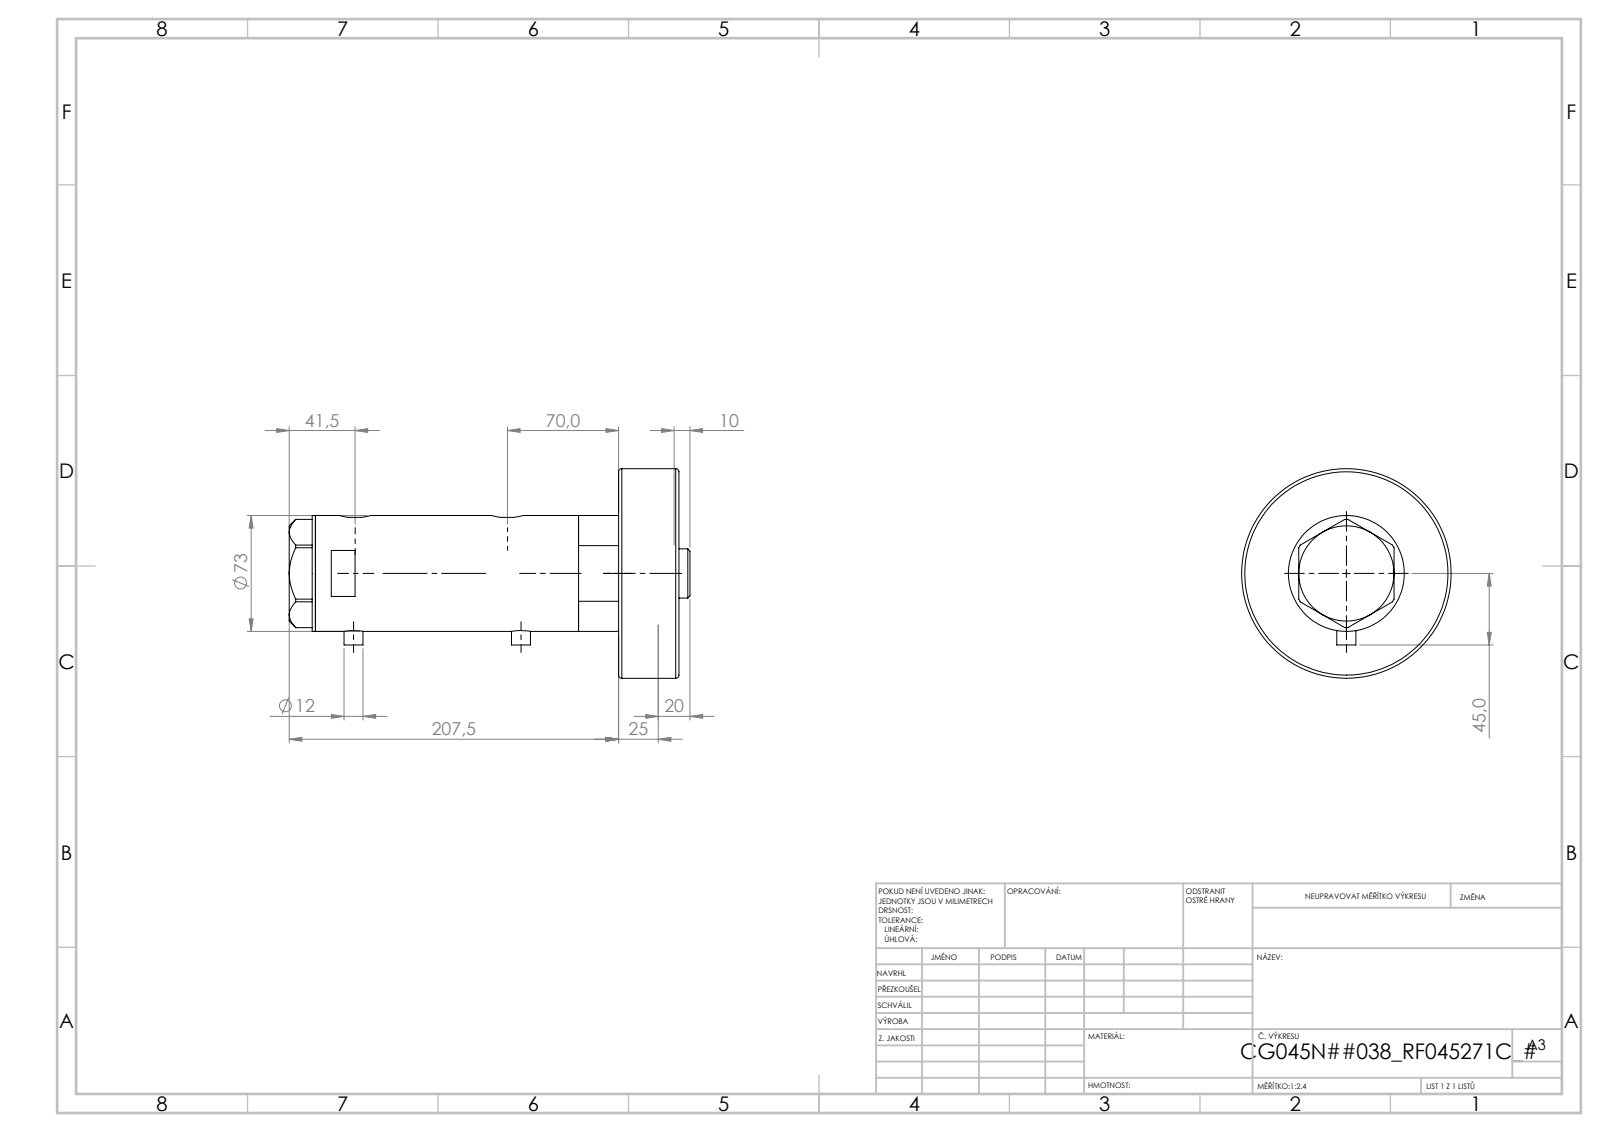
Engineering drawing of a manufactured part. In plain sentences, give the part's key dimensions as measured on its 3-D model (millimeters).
The part is named "V270CG_MIDDLE; V270CG_VC; V270CG_BACK; V270CG_FRONT". Its 3-D file was written by "SolidWorks 2019 (CONFIG_CONTROL_DESIGN)". It is 4 solids with 125 faces: 50 planar, 55 cylindrical and 20 other. Overall it measures 229.52 by 74.1 by 73 millimeters. Its volume is 795 925 cubic millimeters and its surface area 137 847 square millimeters. Round holes: 2 of diameter 5, 2 of diameter 12.5, 2 of diameter 13.16, 1 of diameter 10.5, 1 of diameter 32, 1 of diameter 33.5, 1 of diameter 45, 1 of diameter 48, 1 of diameter 64. Round bosses or shafts: 2 of diameter 12, 1 of diameter 73, 1 of diameter 60, 1 of diameter 58, 1 of diameter 31. Partial cylindrical surfaces (rounded edges, fillets, slot ends): 2 of radius 10. The main face-to-face distances are 105.15, 42.5, 121.65, 79.15, 16.5, 16.51, 26, 25.99, 105.14, 193.02. The hole center spacings are 89.65, 0.99, 1, 8.5, 8.51, 80.15, 81.14, 81.15.
